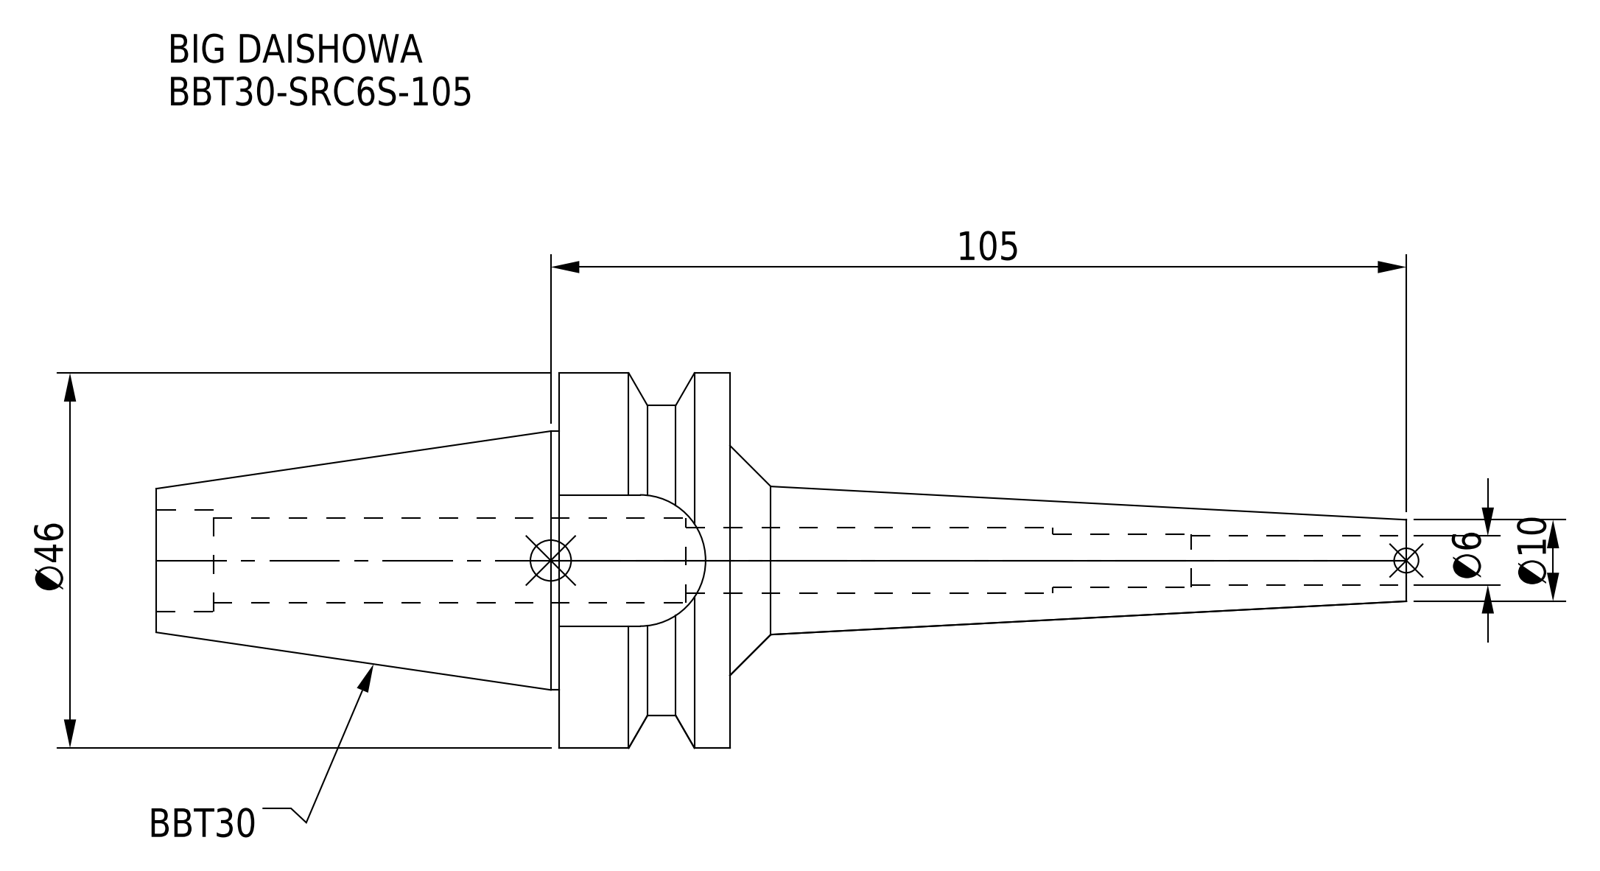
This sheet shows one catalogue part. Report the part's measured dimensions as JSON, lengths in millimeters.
{"part_name": "BBT30-SRC6S-105", "step_written_by": "CREO PARAMETRIC BY PTC INC, 2016380 (AUTOMOTIVE_DESIGN)", "units": "millimeters", "bodies": {"solids": 1, "faces": 46, "planar": 14, "cylindrical": 22, "other": 10}, "overall_size": [153.4, 46, 46], "volume_mm3": 59113, "surface_area_mm2": 17746, "round_holes": [[6, 1], [6.5, 1], [8, 1], [10.4, 1], [12.5, 1]], "round_bosses_or_shafts": [[46, 1], [31.75, 1]], "partial_cylinders_radius": [[8.05, 1], [19, 1]], "face_to_face_distances": [21, 32.6, 70.4, 49.4, 16.1, 83, 104, 153.4, 146.4, 63.4]}
